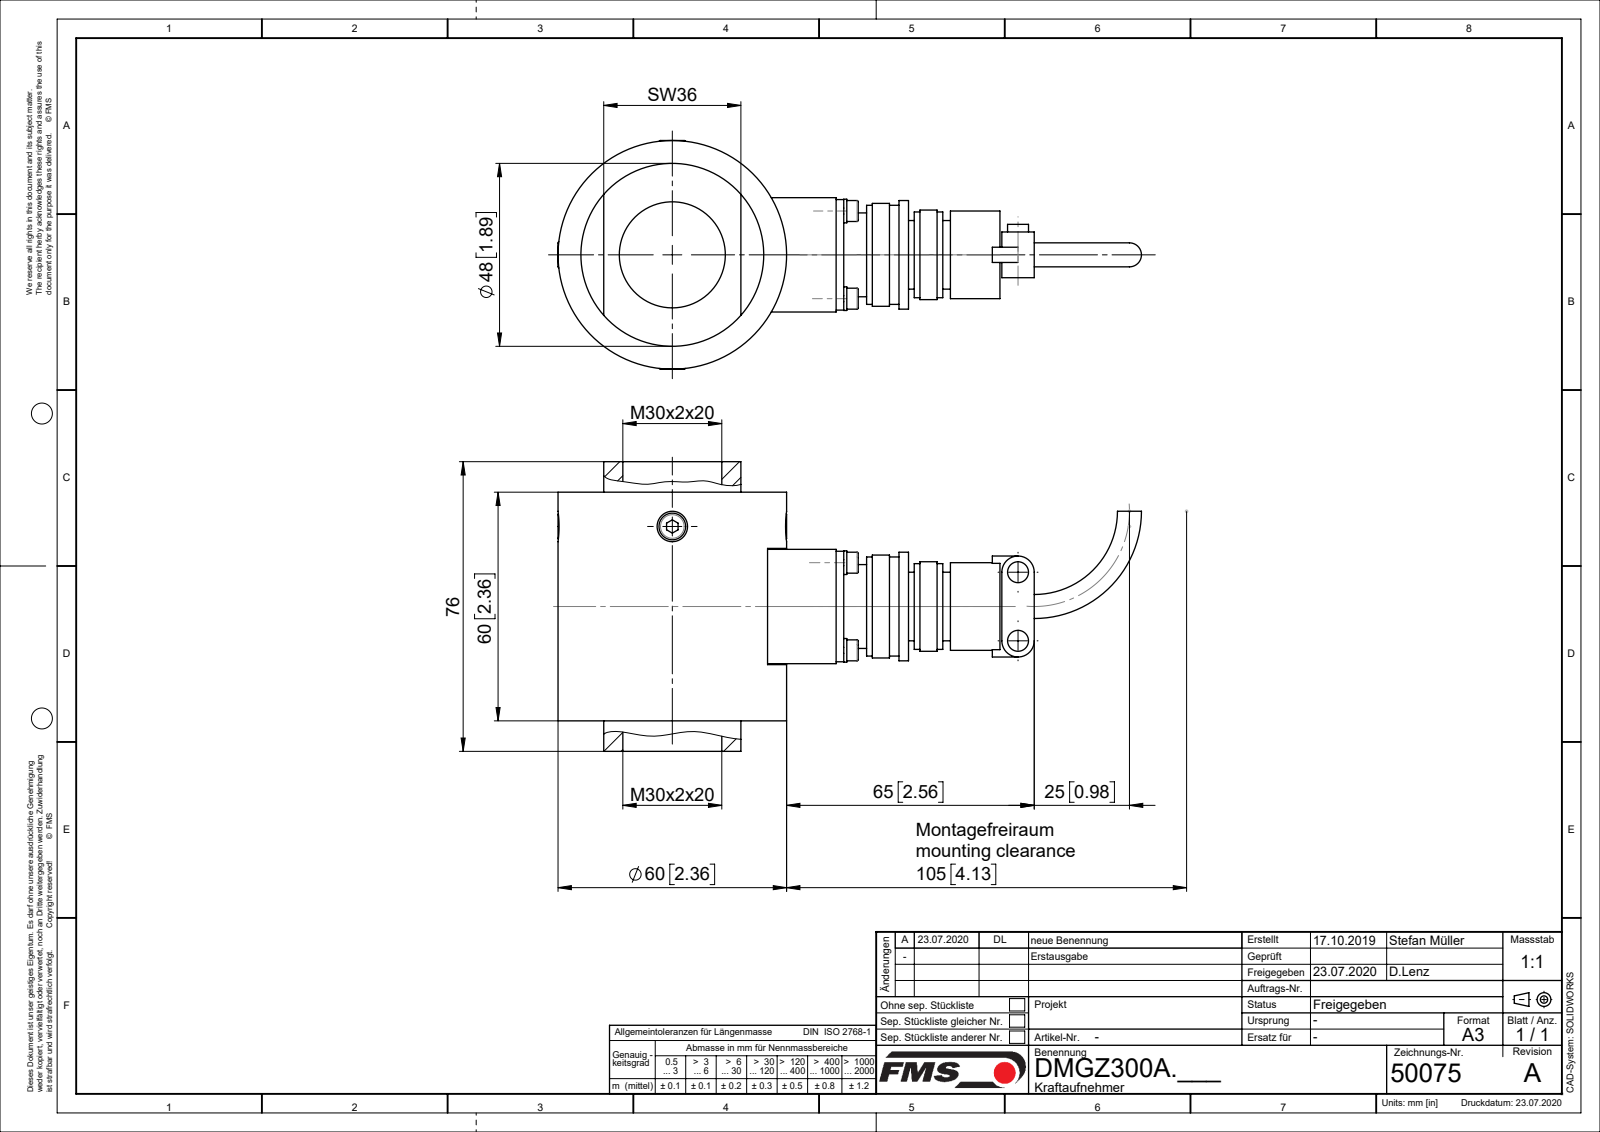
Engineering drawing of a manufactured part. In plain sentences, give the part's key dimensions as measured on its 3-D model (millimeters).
The part is named "D50075; D4948204; TEIL1; D49483 (+6 more)". Its 3-D file was written by "Mechanical Desktop 2007 (CONFIG_CONTROL_DESIGN)". It is 16 solids with 294 faces: 96 planar, 152 cylindrical and 46 other. Overall it measures 153.15 by 76 by 60 millimeters. Its volume is 197 871 cubic millimeters and its surface area 58 062 square millimeters. Round holes: 4 of diameter 2.6, 4 of diameter 3.2, 4 of diameter 3.4, 2 of diameter 3.42, 2 of diameter 4.3, 2 of diameter 8, 1 of diameter 23, 1 of diameter 28.21, 1 of diameter 30.5, 1 of diameter 48. Round bosses or shafts: 6 of diameter 5.5, 4 of diameter 6.2, 4 of diameter 3, 4 of diameter 2.5, 2 of diameter 7, 2 of diameter 4, 1 of diameter 60, 1 of diameter 28.5. Partial cylindrical surfaces (rounded edges, fillets, slot ends): 2 of radius 4.25. The main face-to-face distances are 8, 68, 20, 56, 43, 12, 48, 33, 36, 2. The hole center spacings are 16.26, 23, 14.92, 32.53, 34.47, 21.
